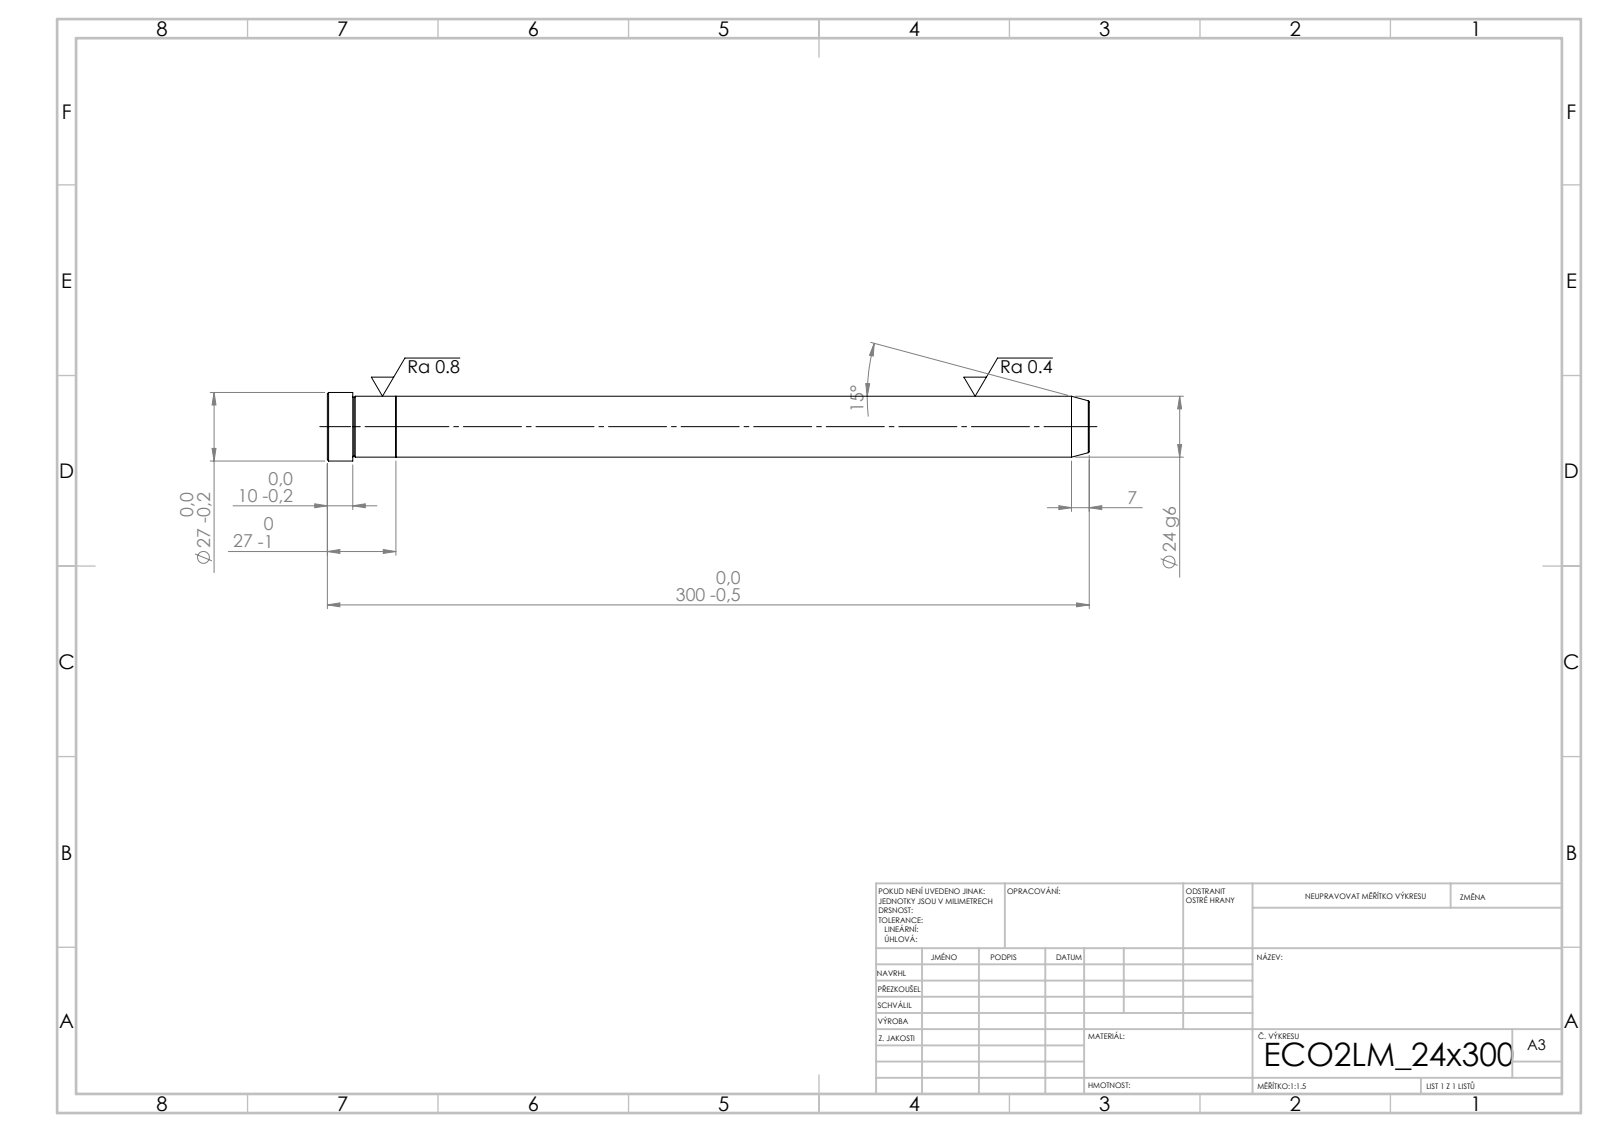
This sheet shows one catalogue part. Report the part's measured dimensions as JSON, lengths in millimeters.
{"step_written_by": "SolidWorks 2019 (CONFIG_CONTROL_DESIGN)", "units": "millimeters", "bodies": {"solids": 2, "faces": 21, "planar": 5, "cylindrical": 6, "other": 10}, "overall_size": [300, 27, 27], "volume_mm3": 136408, "surface_area_mm2": 24617, "round_bosses_or_shafts": [[27, 1], [24, 1]], "face_to_face_distances": [27, 273, 300, 290, 17, 10]}
